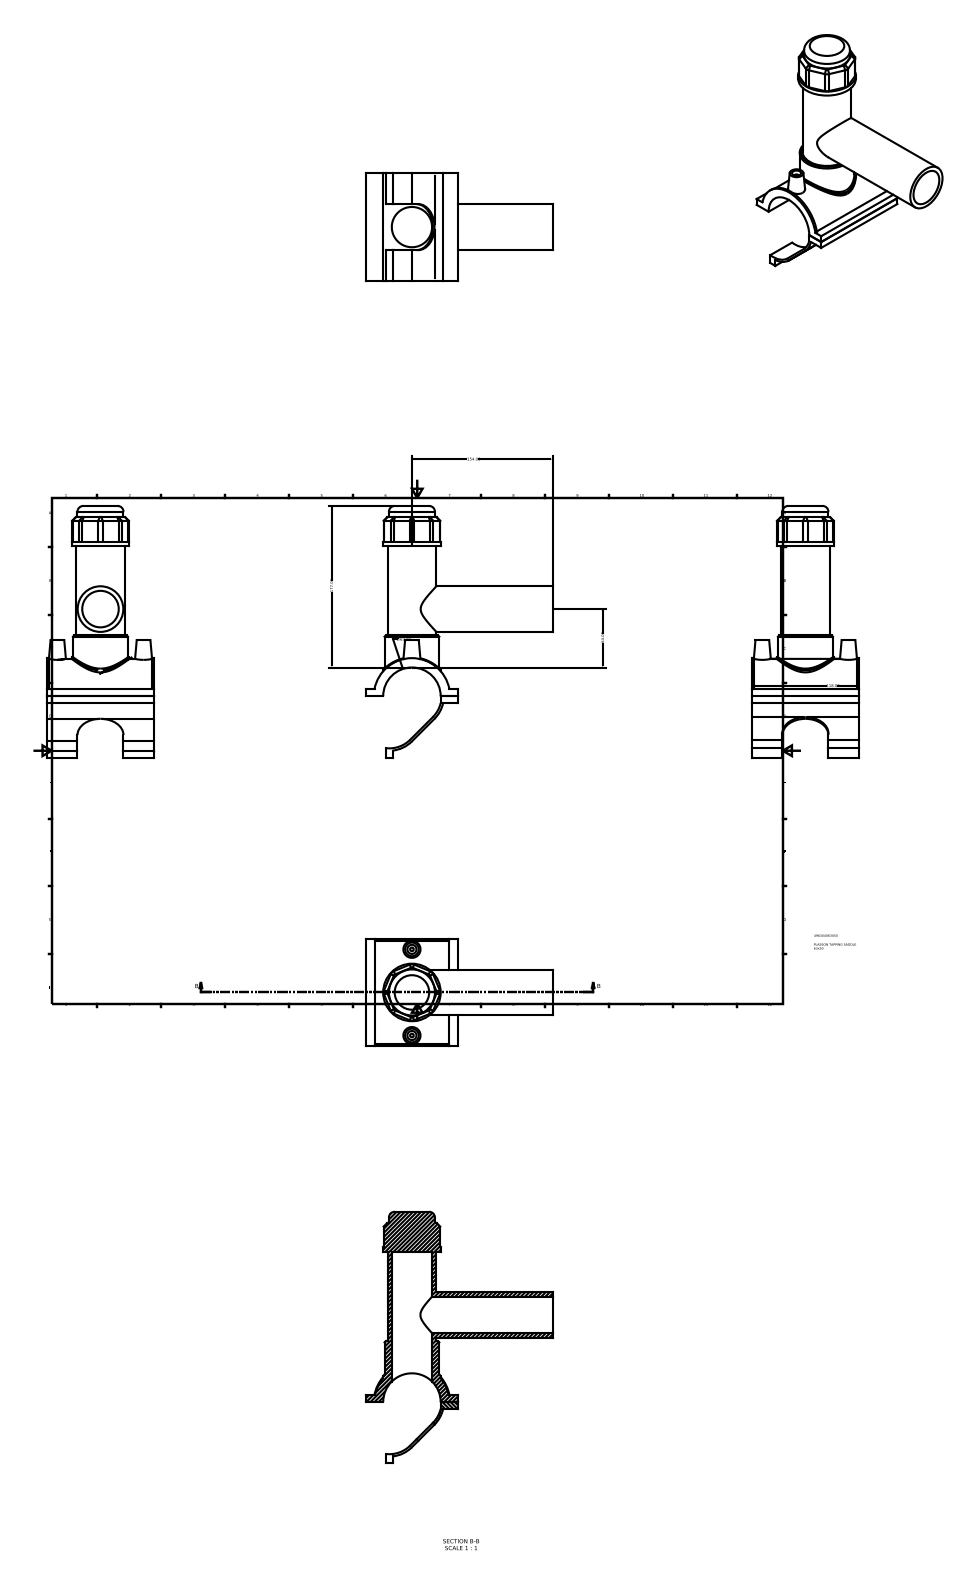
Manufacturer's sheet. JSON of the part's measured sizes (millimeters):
{"part_name": "496304063050", "step_written_by": "Autodesk Inventor 2015 (AUTOMOTIVE_DESIGN)", "units": "millimeters", "bodies": {"solids": 2, "faces": 102, "planar": 57, "cylindrical": 32, "other": 13}, "overall_size": [275.78, 204, 118], "volume_mm3": 486090, "surface_area_mm2": 147057, "round_holes": [[10, 2], [40, 1], [44.1, 1]], "round_bosses_or_shafts": [[4, 2], [63, 1], [59.85, 1], [53.55, 1], [50.4, 1], [50, 1]], "partial_cylinders_radius": [[6.3, 8], [32.38, 2], [34.98, 2], [25.2, 1], [31.5, 1], [40.95, 1], [41.77, 1], [42.59, 1]], "face_to_face_distances": [7.82, 2.6, 164.2, 172.02, 118, 58.22, 7.83, 15.65, 156.37, 15.64], "hole_center_spacings": [47.2, 94.4]}
